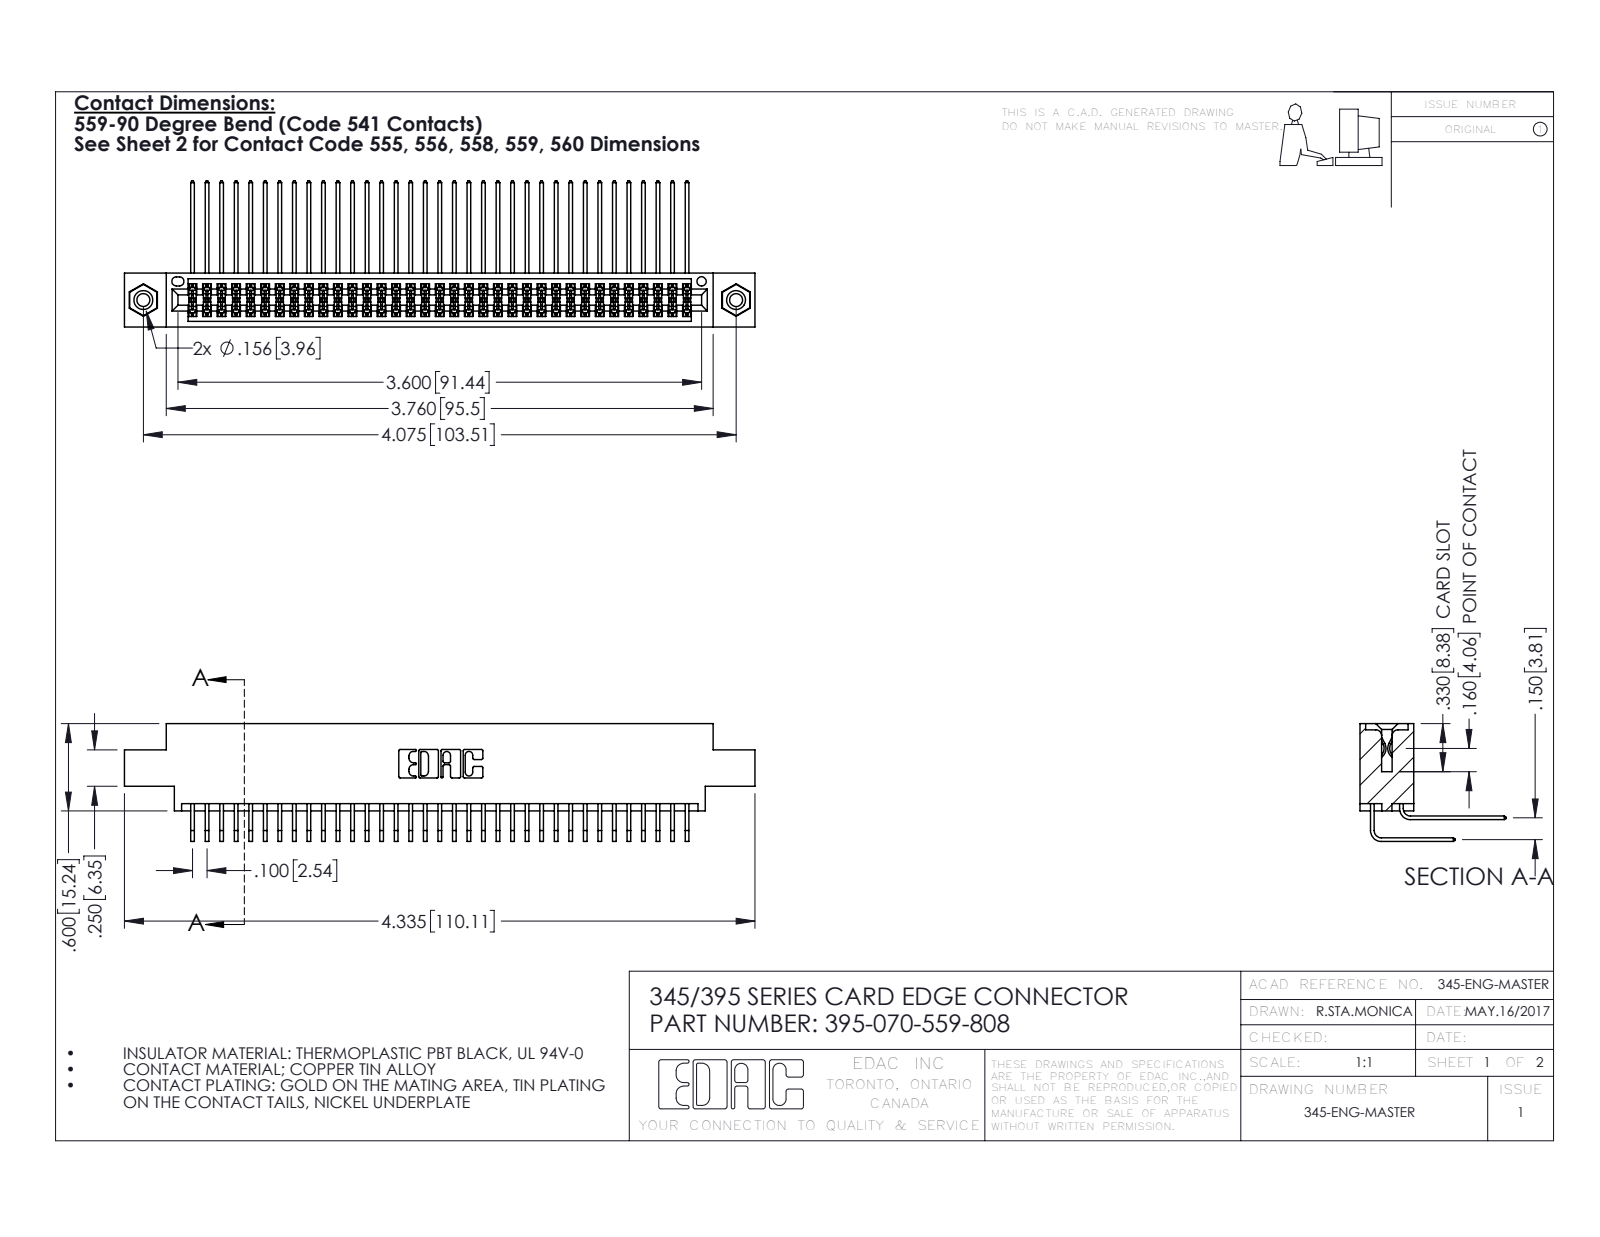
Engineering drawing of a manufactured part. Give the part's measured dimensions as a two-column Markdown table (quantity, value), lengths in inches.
| quantity | value |
| --- | --- |
| part name | 345-292-001_559 Tail - 2; 345-292-001_558 559 Tail - 1; 345 Part_0.170 Offset - 0.156 Dia-TI; 395-070-559-808 (+1 more) |
| STEP written by | SolidWorks 2016 (CONFIG_CONTROL_DESIGN) |
| units | inches |
| bodies | 73 solids, 3830 faces (2566 planar, 1248 cylindrical, 16 other) |
| overall size | 4.335 × 1.005 × 0.809 |
| volume | 0.666 in³ |
| surface area | 27.98 in² |
| round holes (diameter × count) | 0.089 × 2, 0.125 × 2, 0.156 × 2, 0.064 × 1 |
| round bosses / shafts (diameter × count) | 0.155 × 2 |
| partial cylindrical surfaces (radius × count) | 0.006 × 105, 0.01 × 22, 0.007 × 6, 0.031 × 6, 0.026 × 3, 0.014 × 2, 0.019 × 2, 0.022 × 2 |
| main face-to-face distances | 0.072, 0.298, 0.37, 0.2, 0.098, 0.272, 0.025, 0.225, 0.175, 0.15 |
| hole center spacings | 0.27, 3.839, 4.075 |
